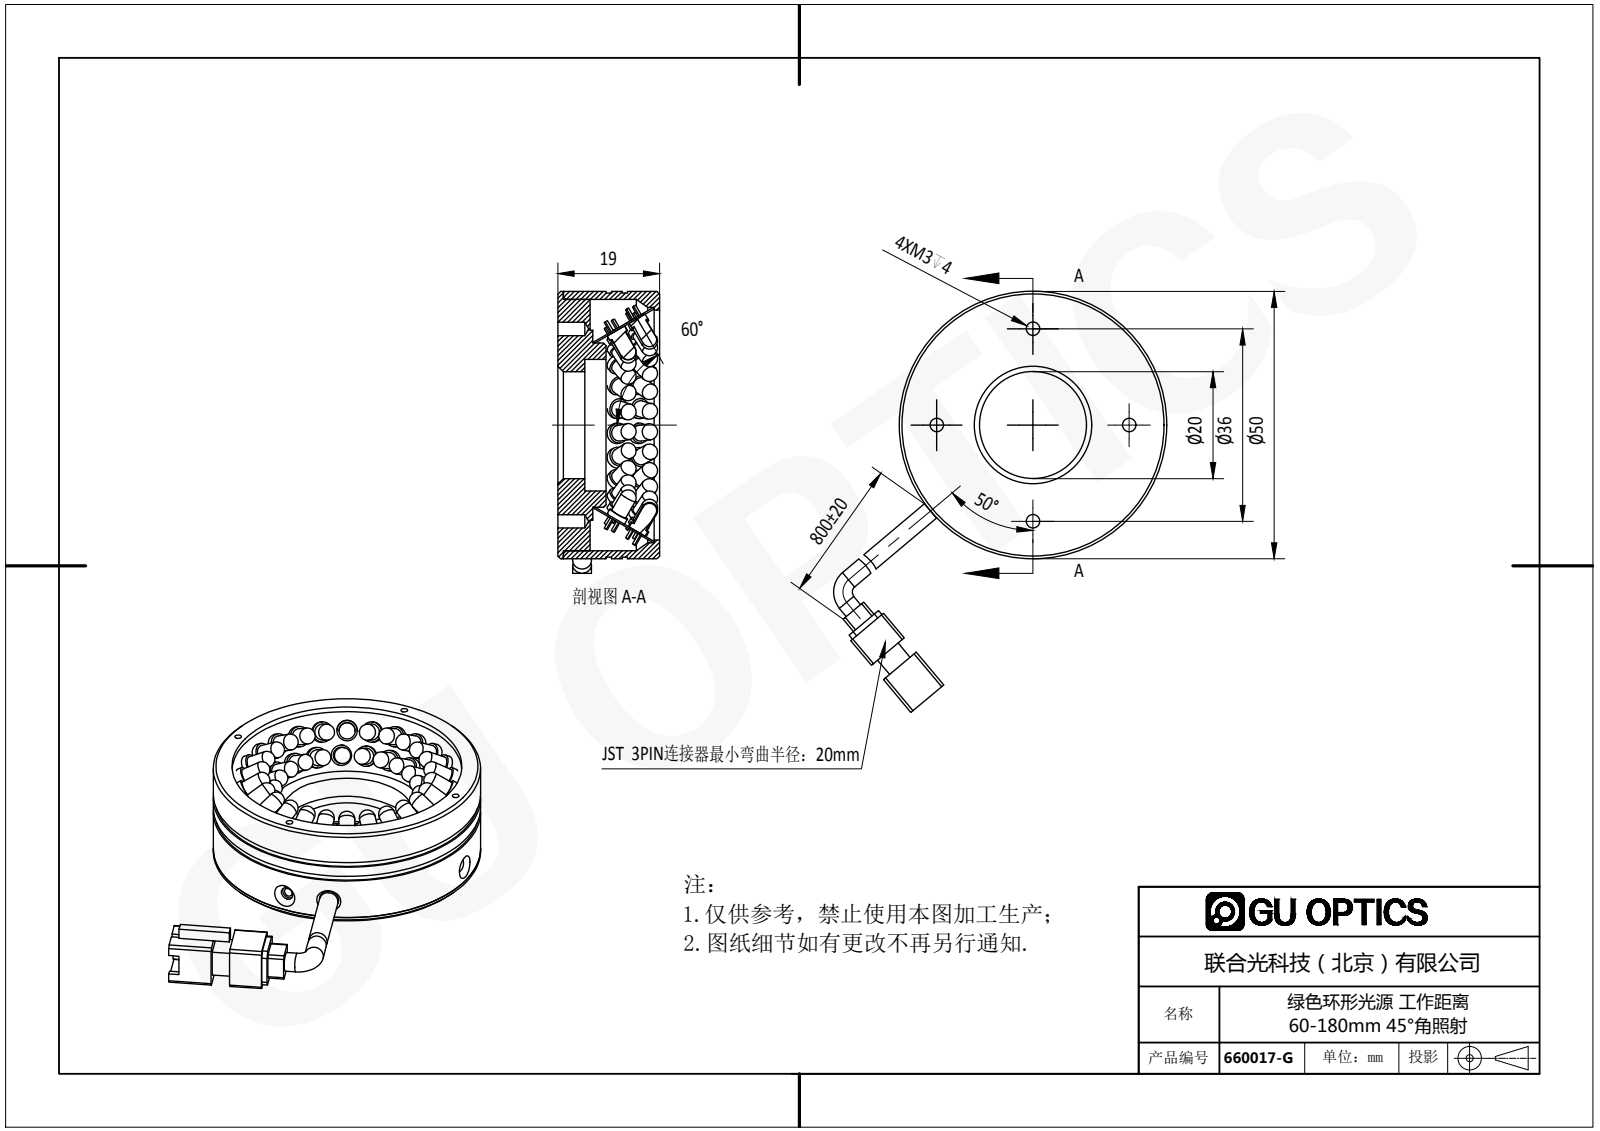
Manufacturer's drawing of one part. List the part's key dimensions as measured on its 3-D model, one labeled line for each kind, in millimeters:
Part name (STEP PRODUCT): 660017-G
STEP written by: SolidWorks 2016 (AUTOMOTIVE_DESIGN)
Units: millimetres
Bodies: 54 solids, 1066 faces (662 planar, 300 cylindrical, 104 other)
Overall size (bounding box): 82.93 × 50 × 19
Volume: 17 639 mm³ · Surface area: 20 260 mm²
Round holes (diameter × count): ⌀1.25 ×4, ⌀2.5 ×4, ⌀1.6 ×2, ⌀2.4 ×2, ⌀3 ×2, ⌀3.6 ×1, ⌀20 ×1, ⌀24.6 ×1, ⌀43 ×1, ⌀44 ×1
Round bosses / shafts (diameter × count): ⌀3.8 ×49, ⌀3 ×47, ⌀3.5 ×2, ⌀50 ×1, ⌀49.4 ×1, ⌀47 ×1, ⌀35.54 ×1, ⌀30.72 ×1
Partial cylindrical surfaces — rounded edges, fillets, slot ends (radius × count): R0.5 ×12, R1 ×4, R4 ×1
Main face-to-face distances: 1, 6, 0.5, 5, 5.5, 8, 3, 13, 2.5, 1.5
Hole centre spacings: 11.66, 20.95, 23, 32.53, 18, 25.46, 35.6, 39.63
